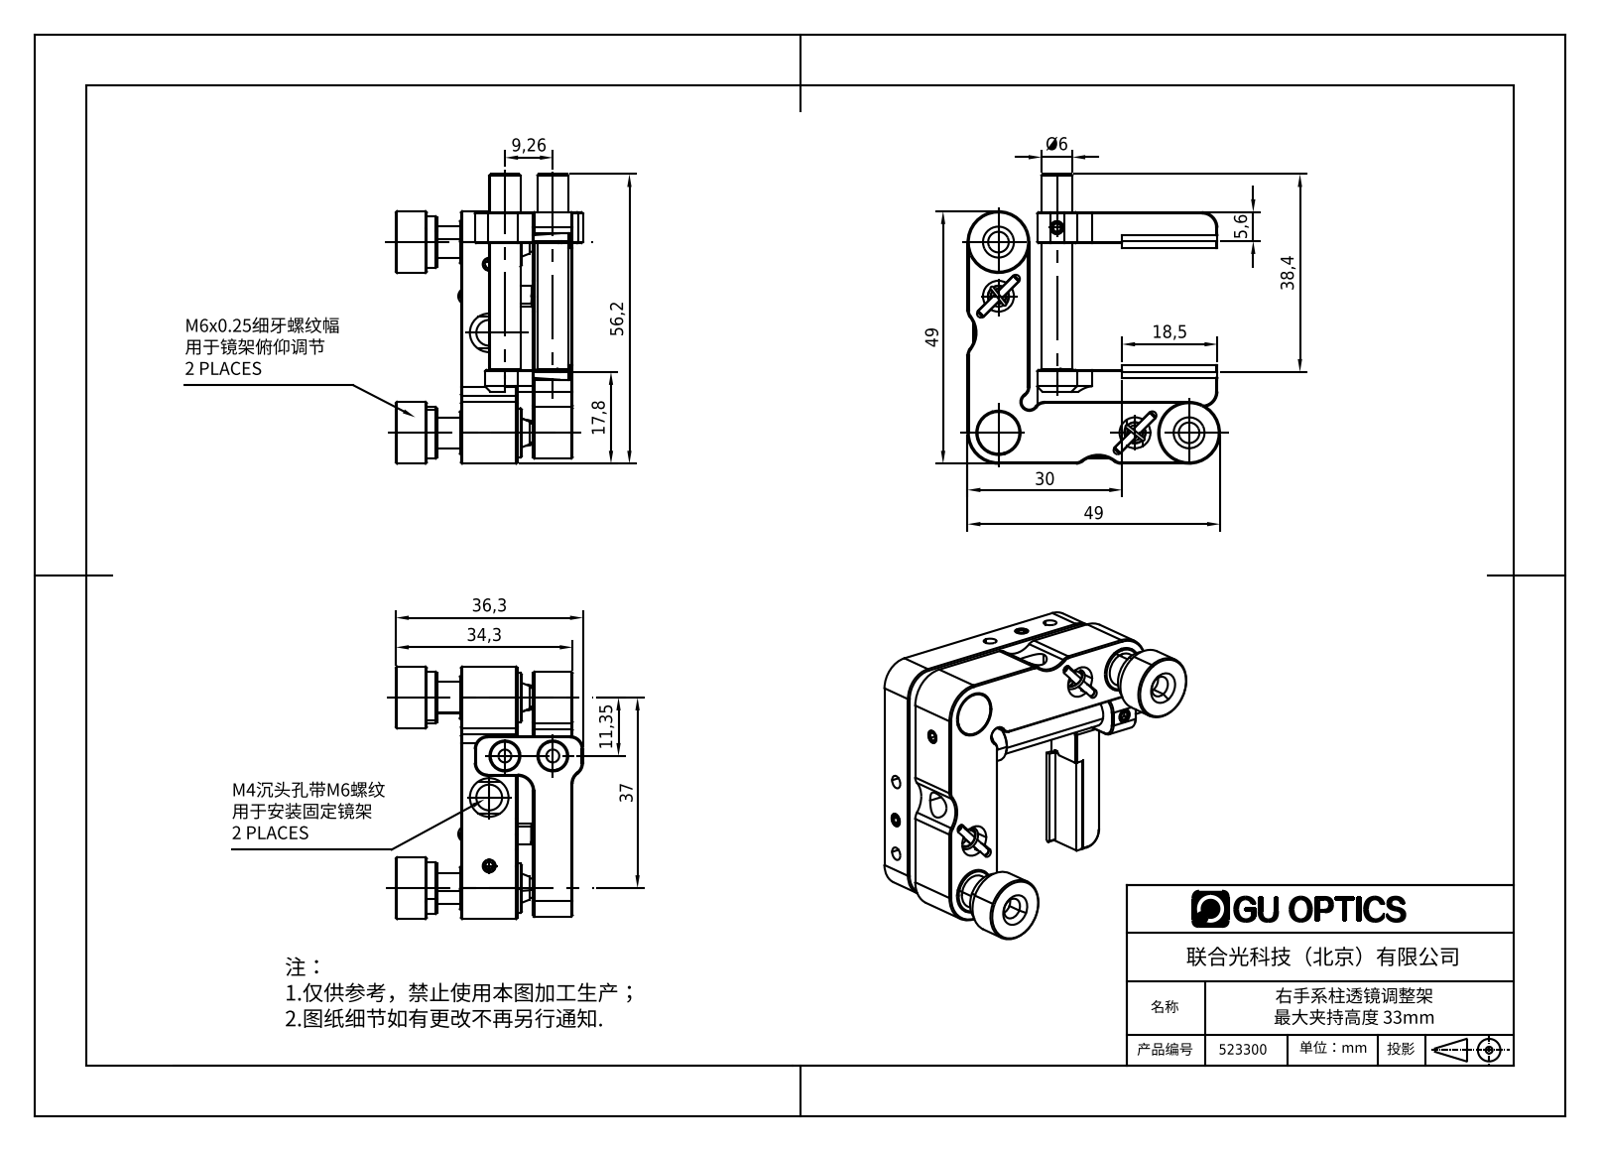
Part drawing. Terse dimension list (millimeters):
name: 523300
written by: SolidWorks 2020 (CONFIG_CONTROL_DESIGN)
unit: mm
bodies: 0 solids, 840 faces (475 planar, 234 cylindrical, 131 other)
size: 58.2 × 52 × 38.02
holes: 4× ⌀2.5, 4× ⌀6, 2× ⌀5, 2× ⌀8, 2× ⌀9.8, 2× ⌀12
bosses: 4× ⌀6, 2× ⌀9.5, 2× ⌀8.6, 2× ⌀4, 2× ⌀2, 2× ⌀1.5, 1× ⌀5.8, 1× ⌀5.2
rounds: 10× R2, 5× R2.5, 5× R5.5, 4× R1.1, 4× R1.25, 4× R3, 3× R0.8, 2× R3.85
face distances: 11, 7.7, 11.5, 0.5, 3.5, 11.2, 22.2, 14.5, 12, 1.5
hole spacings: 5, 10.5, 45.51, 8.8, 9.3, 13.52, 15.16, 18.31
